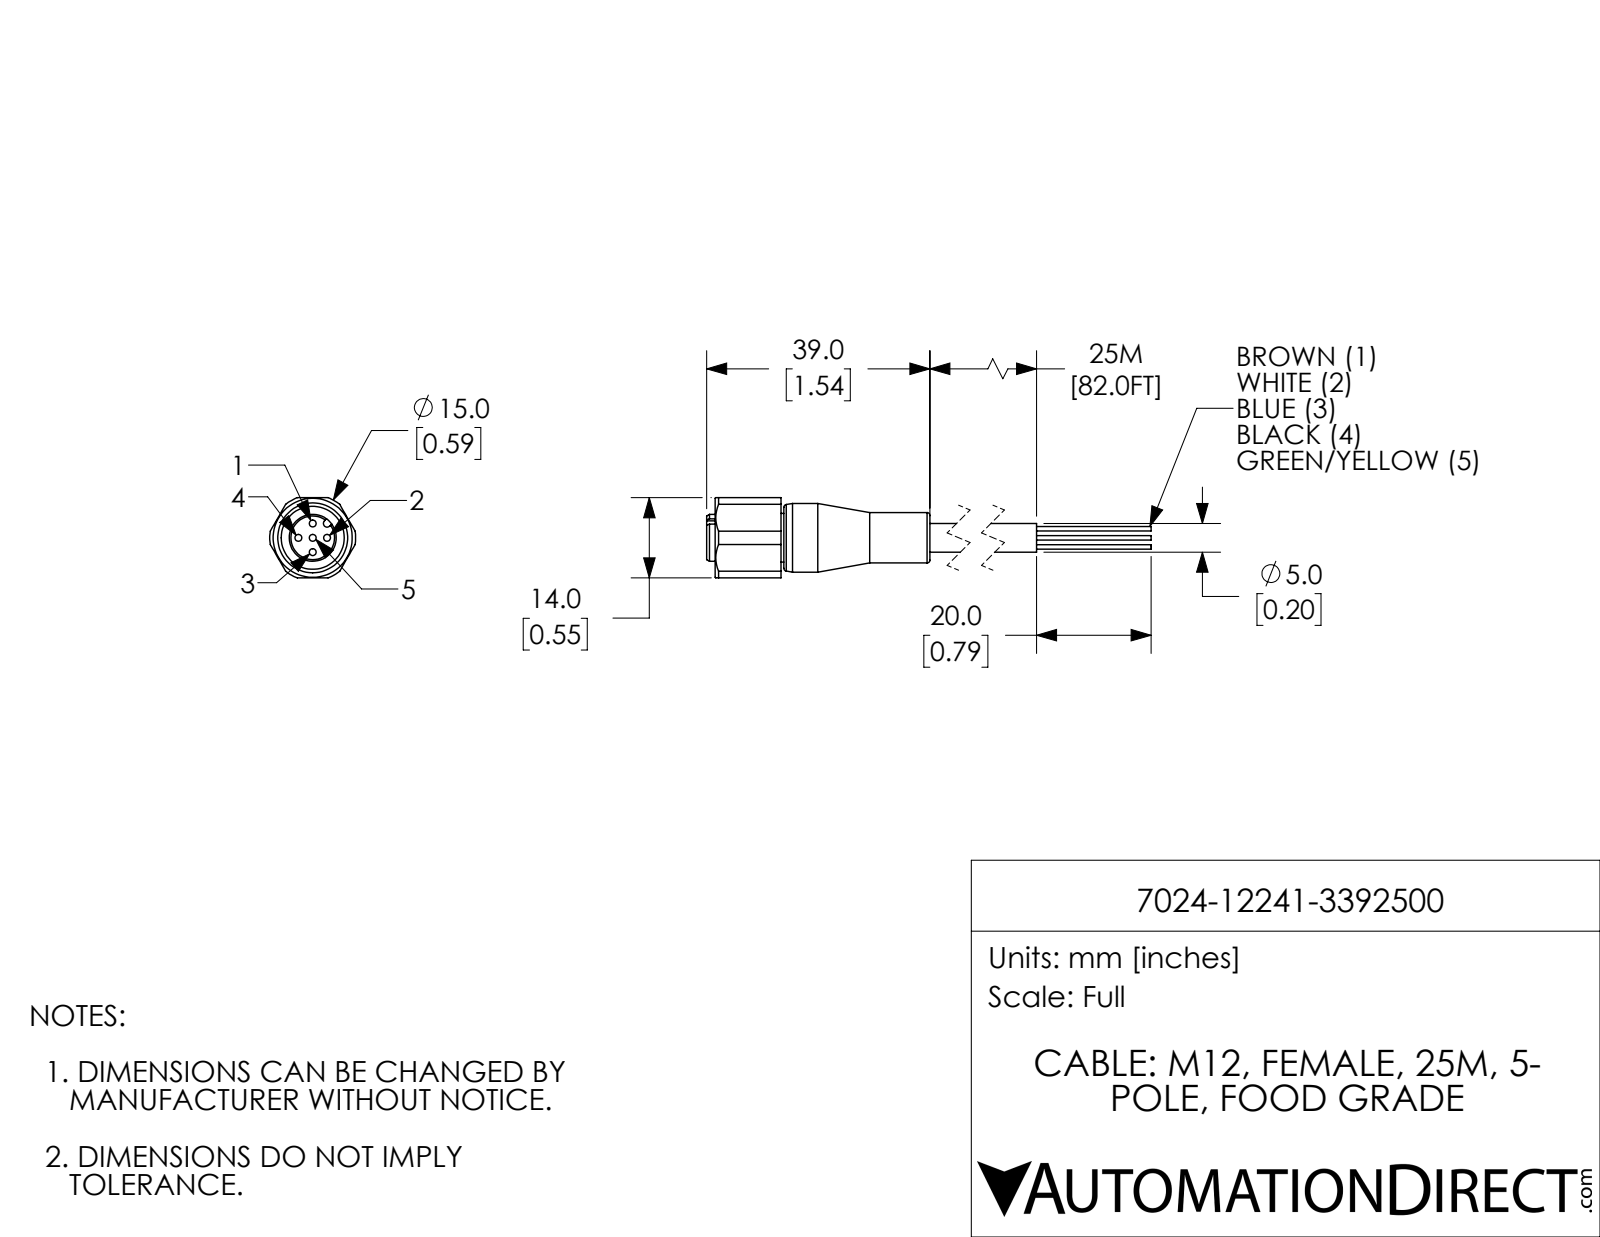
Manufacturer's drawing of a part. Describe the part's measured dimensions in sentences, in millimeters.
The part is named "7024-12241-3392500". Its 3-D file was written by "SolidWorks 2018 (AUTOMOTIVE_DESIGN)". It is 1 solid with 80 faces: 26 planar, 39 cylindrical and 15 other. Overall it measures 77.8 by 15 by 14 millimeters. Its volume is 4 125 cubic millimeters and its surface area 2 876 square millimeters. Round holes: 5 of diameter 1.2, 1 of diameter 11. Round bosses or shafts: 5 of diameter 0.76, 1 of diameter 12, 1 of diameter 8.8, 1 of diameter 8.5, 1 of diameter 8.2, 1 of diameter 5. Partial cylindrical surfaces (rounded edges, fillets, slot ends): 1 of radius 0.65, 1 of radius 7.5. The main face-to-face distances are 14, 4, 9, 13, 1.5, 7.5, 11.5, 13.5, 12, 4.5. The hole center spacings are 2.5, 3.54, 5.
